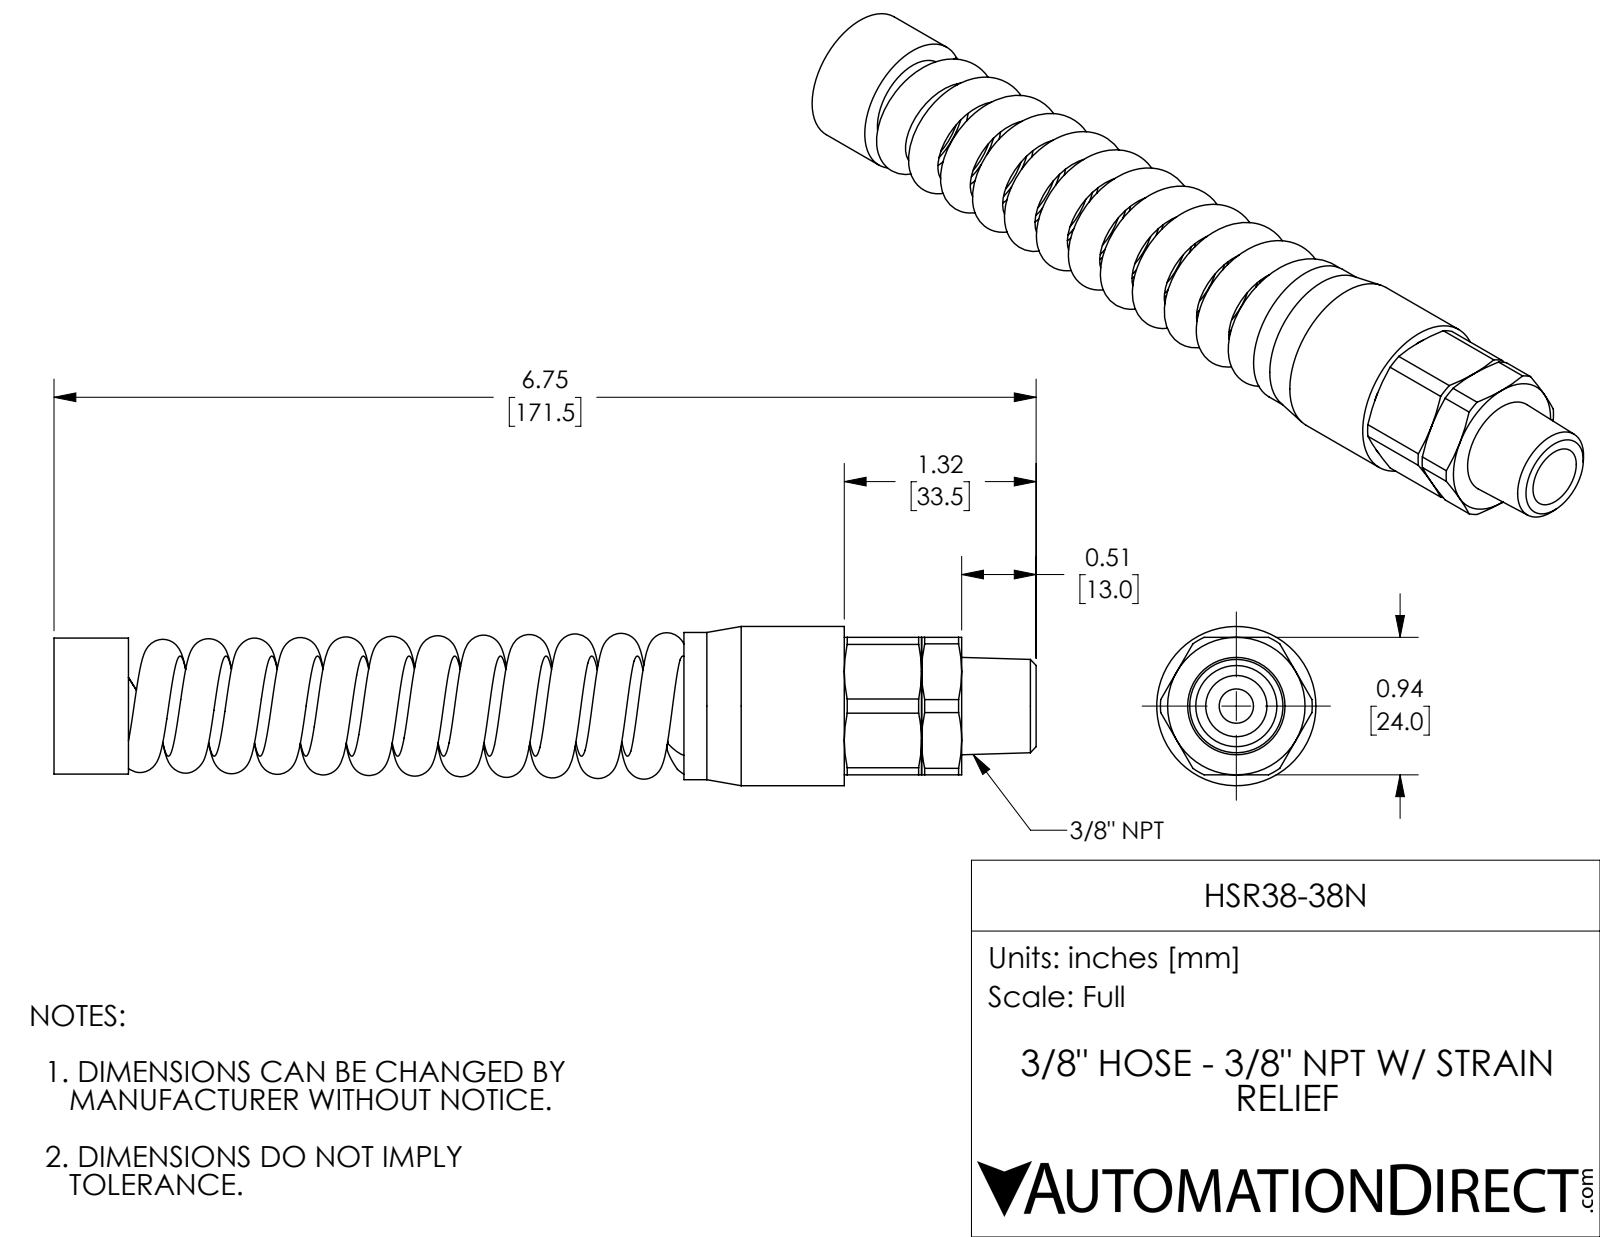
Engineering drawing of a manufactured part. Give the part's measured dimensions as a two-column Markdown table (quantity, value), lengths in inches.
| quantity | value |
| --- | --- |
| part name | HSR38-38N |
| STEP written by | SolidWorks 2017 (AUTOMOTIVE_DESIGN) |
| units | inches |
| bodies | 3 solids, 139 faces (35 planar, 65 cylindrical, 39 other) |
| overall size | 6.752 × 1.094 × 1.094 |
| volume | 2.252 in³ |
| surface area | 44.47 in² |
| round holes (diameter × count) | 0.236 × 1, 0.421 × 1, 0.63 × 1, 0.689 × 1, 0.787 × 1, 0.866 × 1, 0.945 × 1 |
| round bosses / shafts (diameter × count) | 1.094 × 1, 1.012 × 1, 0.935 × 1, 0.933 × 1, 0.846 × 1, 0.413 × 1 |
| partial cylindrical surfaces (radius × count) | 0.52 × 1, 0.522 × 1 |
| main face-to-face distances | 0.945, 0.512, 6.24, 4.744, 0.453, 0.728, 0.276, 1.496, 5.512, 5.965 |
